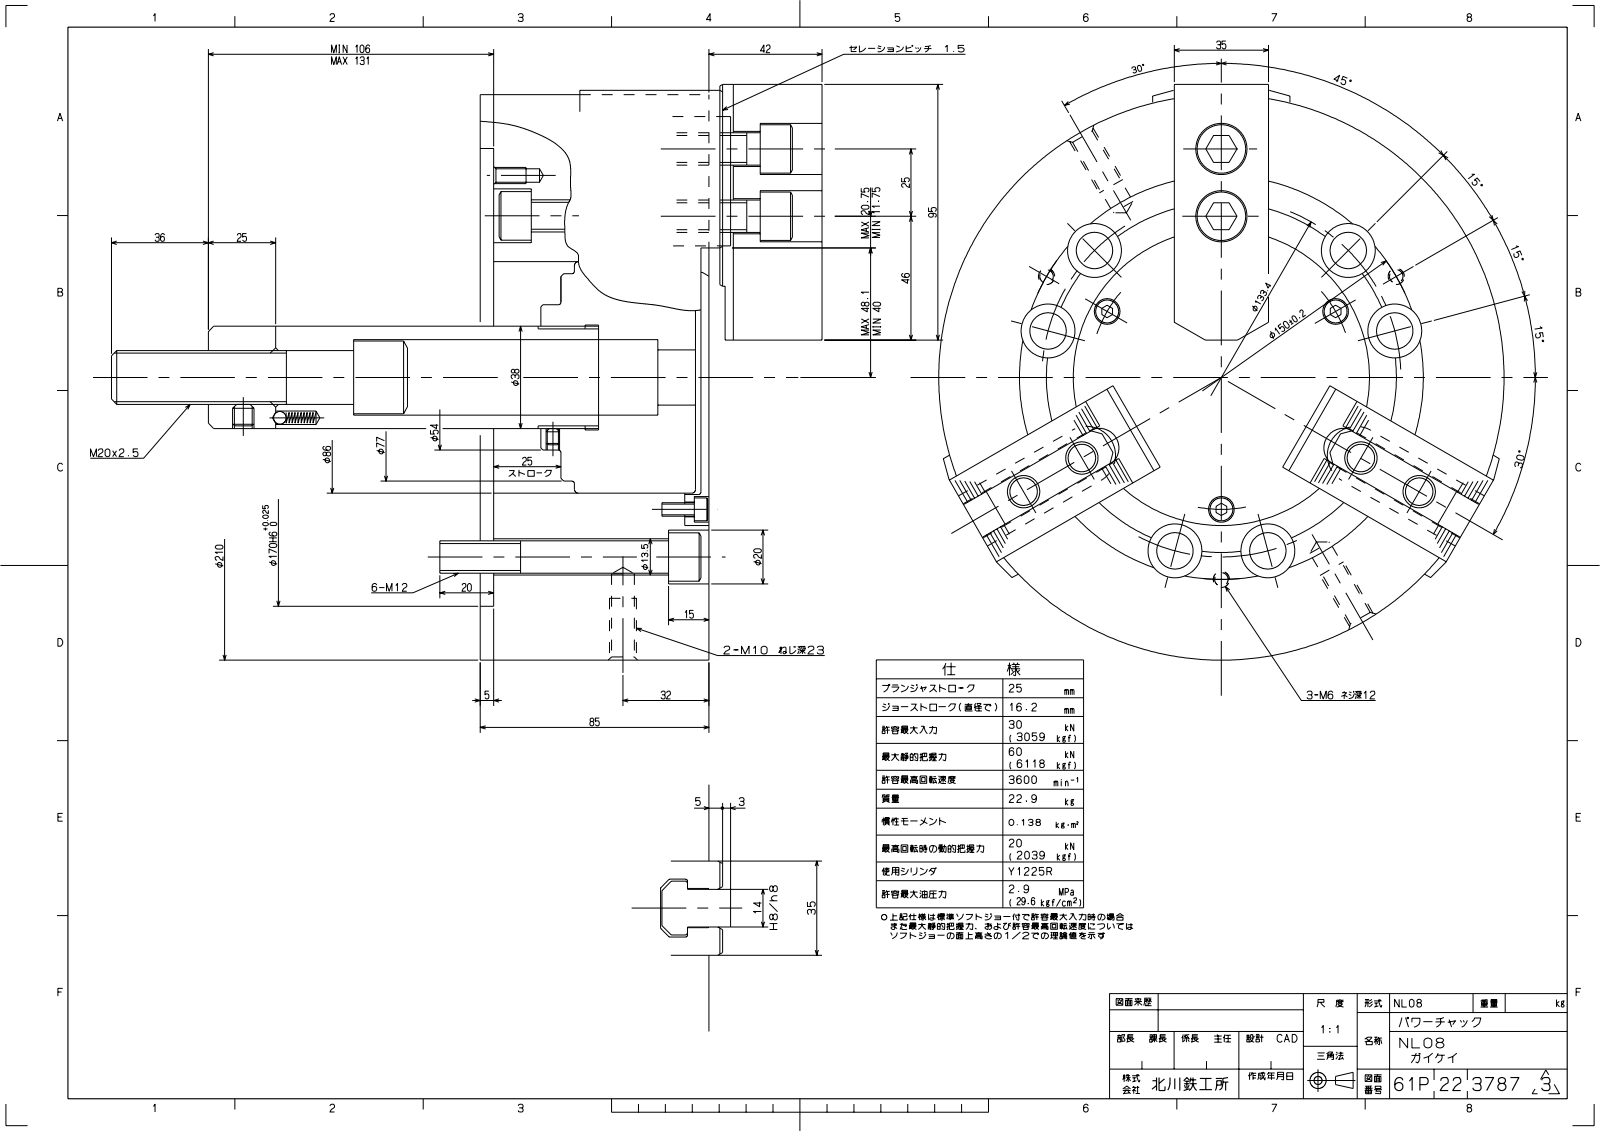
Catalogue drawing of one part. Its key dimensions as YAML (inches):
part_name: "61P211226_NL08_ASSY"
step_written_by: "ST-DEVELOPER v16.7 (AUTOMOTIVE_DESIGN)"
units: inches
bodies: {solids: 27, faces: 2525, planar: 2274, cylindrical: 138, other: 113}
overall_size: [10.402, 8.774, 8.702]
volume: 179.7
surface_area: 708.2
round_holes:
  - {diameter: 0.197, count: 13}
  - {diameter: 0.787, count: 10}
  - {diameter: 0.472, count: 9}
  - {diameter: 0.531, count: 9}
  - {diameter: 0.236, count: 6}
  - {diameter: 0.512, count: 6}
  - {diameter: 0.748, count: 6}
  - {diameter: 0.165, count: 3}
  - {diameter: 0.217, count: 3}
  - {diameter: 0.374, count: 3}
  - {diameter: 0.591, count: 3}
  - {diameter: 0.315, count: 1}
round_bosses_or_shafts:
  - {diameter: 0.709, count: 9}
  - {diameter: 0.335, count: 3}
  - {diameter: 8.268, count: 1}
  - {diameter: 3.386, count: 1}
  - {diameter: 2.126, count: 1}
  - {diameter: 1.496, count: 1}
  - {diameter: 1.063, count: 1}
partial_cylinders:
  - {radius: 0.167, count: 6}
  - {radius: 0.287, count: 3}
  - {radius: 0.423, count: 3}
  - {radius: 1.516, count: 1}
  - {radius: 1.713, count: 1}
  - {radius: 2.165, count: 1}
face_to_face_distances: [1.378, 3.15, 0.197, 0.315, 1.575, 3.346, 1.22, 1.693, 0.118, 1.386]
hole_center_spacings: [4.216, 0.911, 2.706, 3.638, 4.259, 4.43, 1.929, 5.291]
